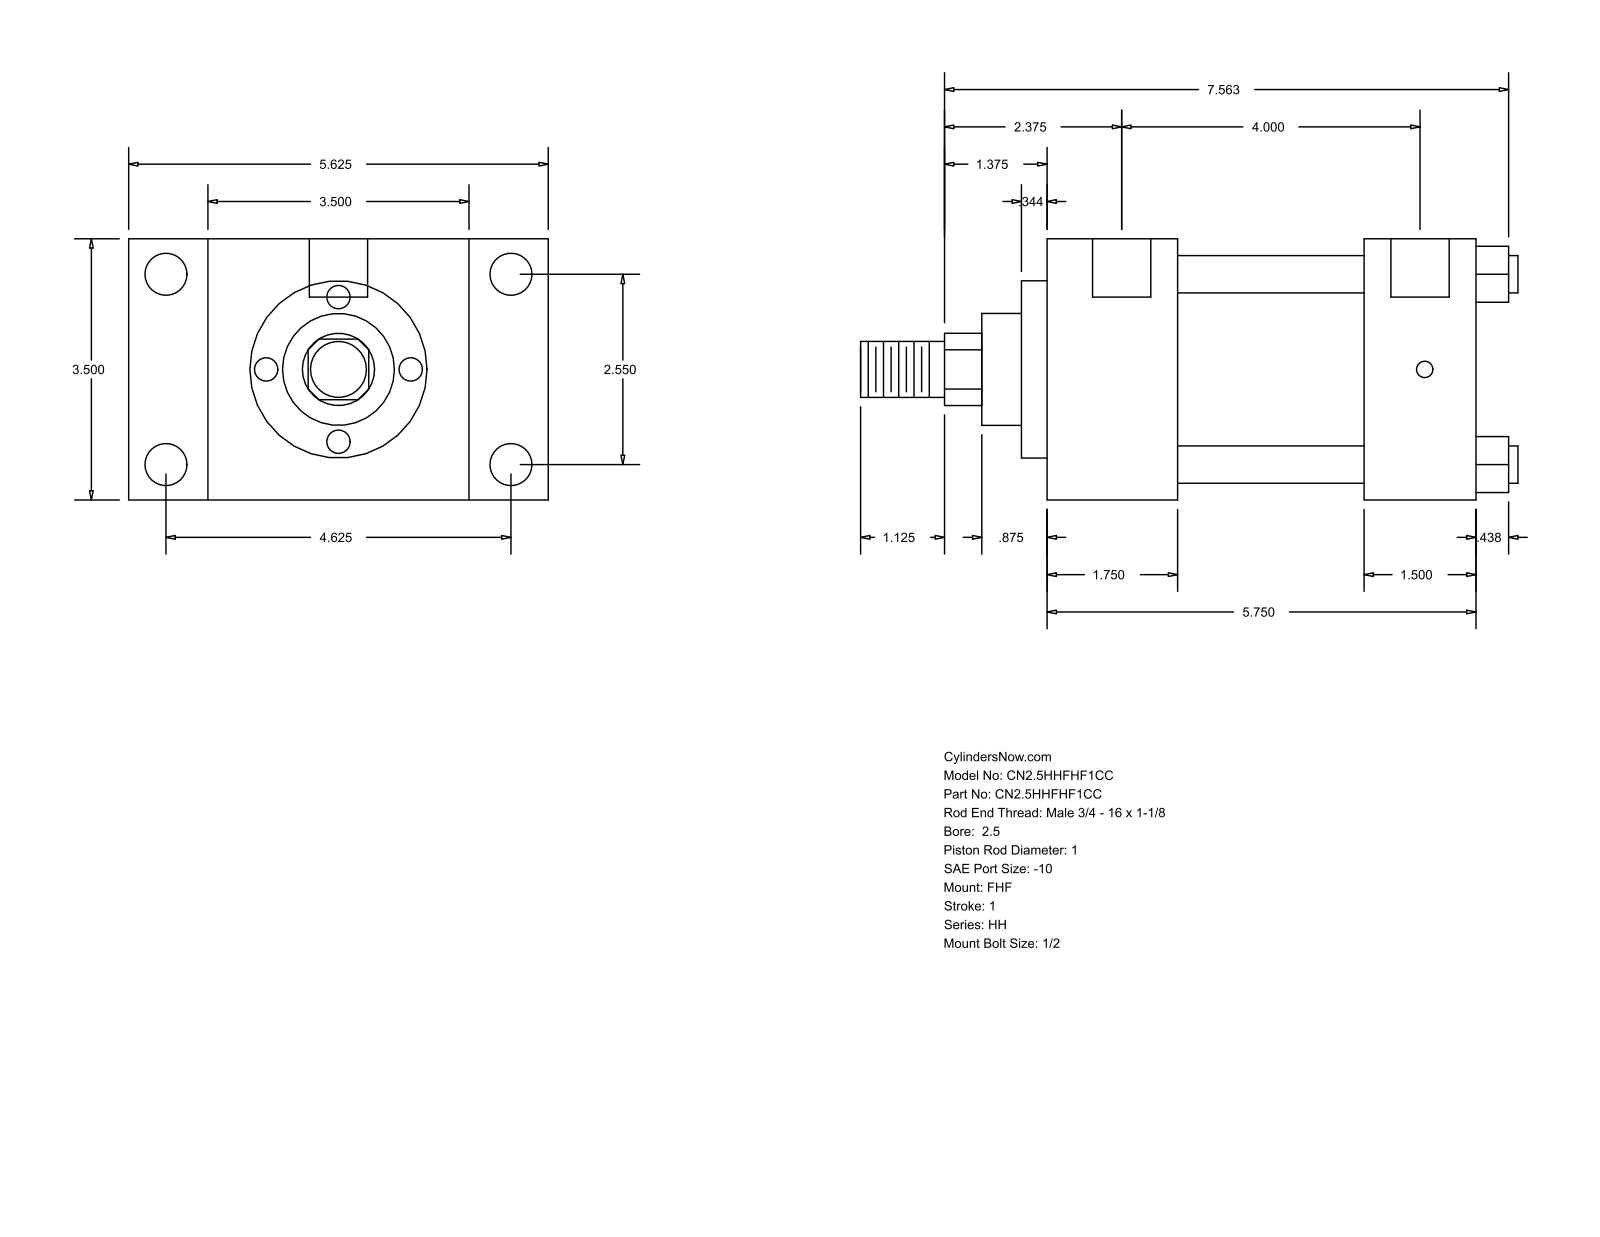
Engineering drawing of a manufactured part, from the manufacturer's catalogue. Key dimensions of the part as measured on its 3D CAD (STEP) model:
Part name (STEP PRODUCT): HH_FHF__0250_1
STEP written by: GSSL Pune (CONFIG_CONTROL_DESIGN)
Units: millimetres
Bodies: 0 solids, 90 faces (61 planar, 29 cylindrical, 0 other)
Overall size (bounding box): 223.84 × 142.88 × 88.9
Round holes (diameter × count): ⌀5.56 ×4, ⌀14.3 ×4, ⌀19.84 ×2
Round bosses / shafts (diameter × count): ⌀12.7 ×4, ⌀73.03 ×1, ⌀60.33 ×1, ⌀38.1 ×1, ⌀25.4 ×1, ⌀19.05 ×1
Partial cylindrical surfaces — rounded edges, fillets, slot ends (radius × count): R12.29 ×1
Main face-to-face distances: 88.9, 44.46, 26.99, 115.89, 146.05, 101.59, 142.88, 107.96, 63.5, 38.09
Hole centre spacings: 64.76, 104.77, 117.48, 134.15, 1.58, 1.59, 101.6, 103.18
